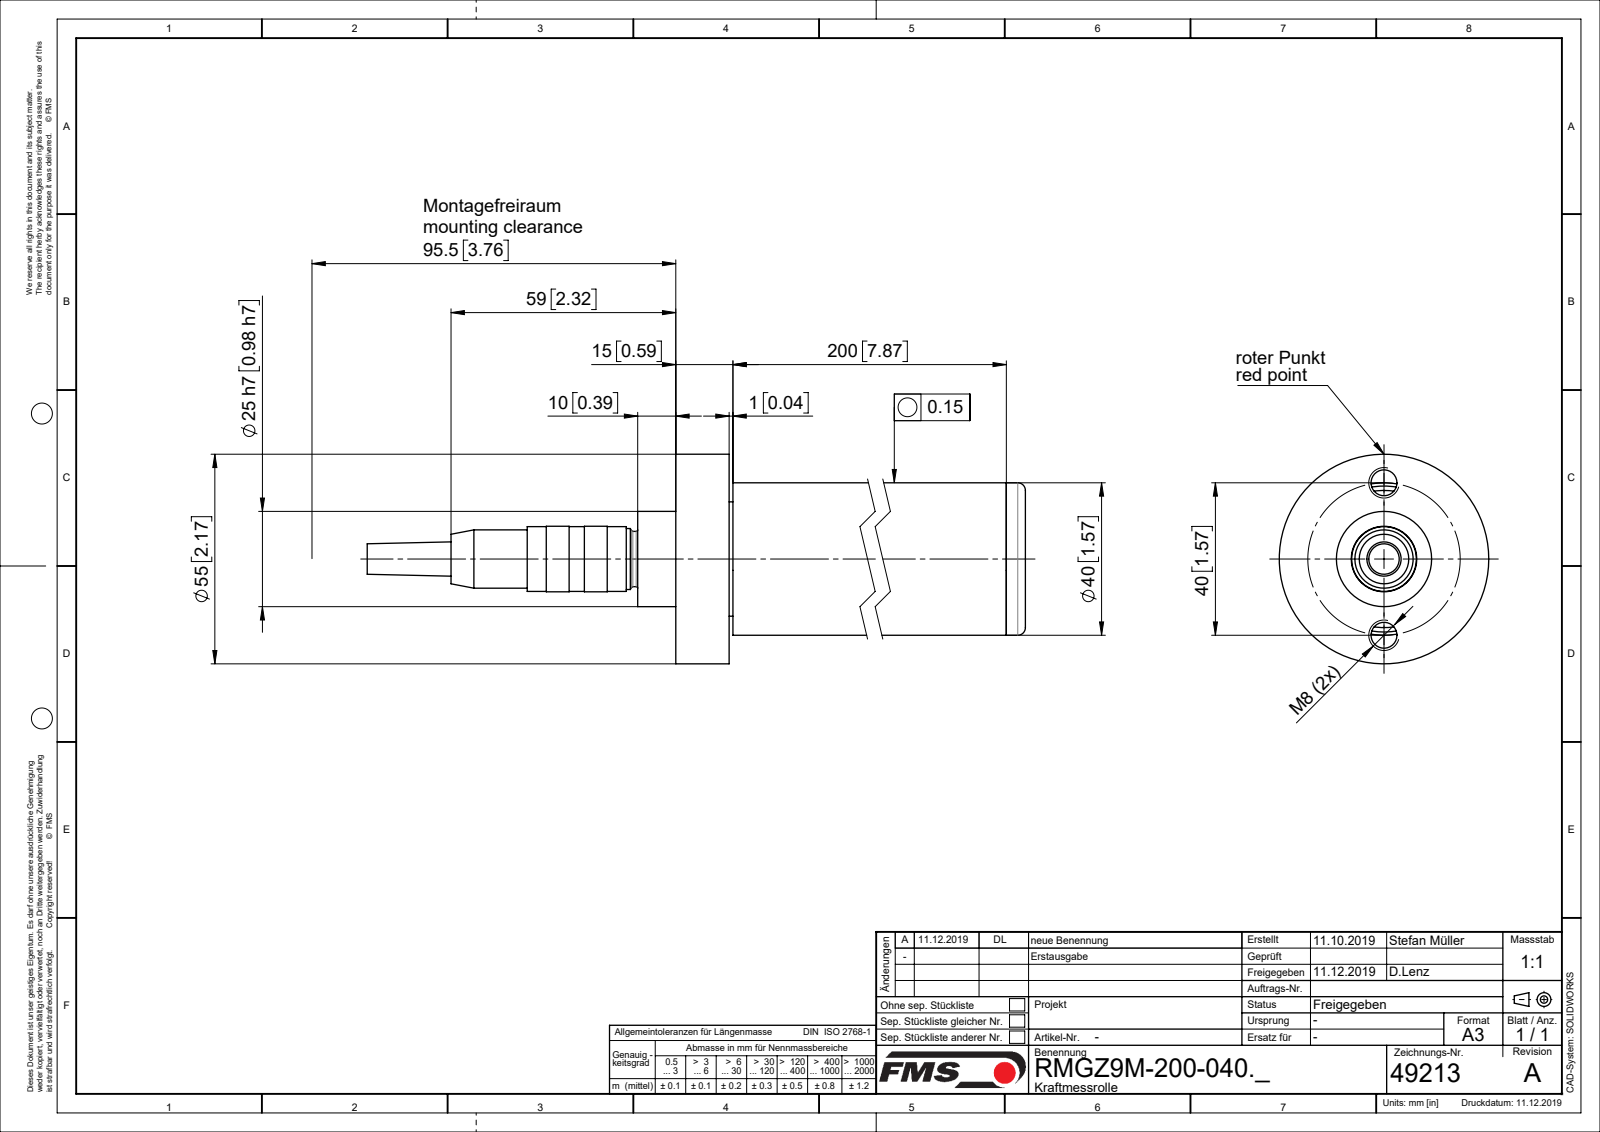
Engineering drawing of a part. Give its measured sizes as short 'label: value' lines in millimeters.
name: R49213; R4862004; TEIL1; RILLENKUGELLAGER_6201 (+4 more)
written by: Mechanical Desktop 2007 (CONFIG_CONTROL_DESIGN)
unit: mm
bodies: 7 solids, 225 faces (63 planar, 100 cylindrical, 62 other)
size: 301 × 55 × 55
volume: 152 712 mm³; area: 84 656 mm²
holes: 2× ⌀6.91, 1× ⌀10, 1× ⌀11.5, 1× ⌀12, 1× ⌀13.3, 1× ⌀14, 1× ⌀26.3, 1× ⌀27, 1× ⌀28, 1× ⌀32, 1× ⌀36
bosses: 1× ⌀55, 1× ⌀40, 1× ⌀31.3, 1× ⌀25, 1× ⌀17.5, 1× ⌀17.2, 1× ⌀17, 1× ⌀16
rounds: 1× R10.5
face distances: 14, 16, 7.4, 2.6, 14.5, 4.5, 219.5, 205.5, 30, 10
hole spacings: 20, 40
